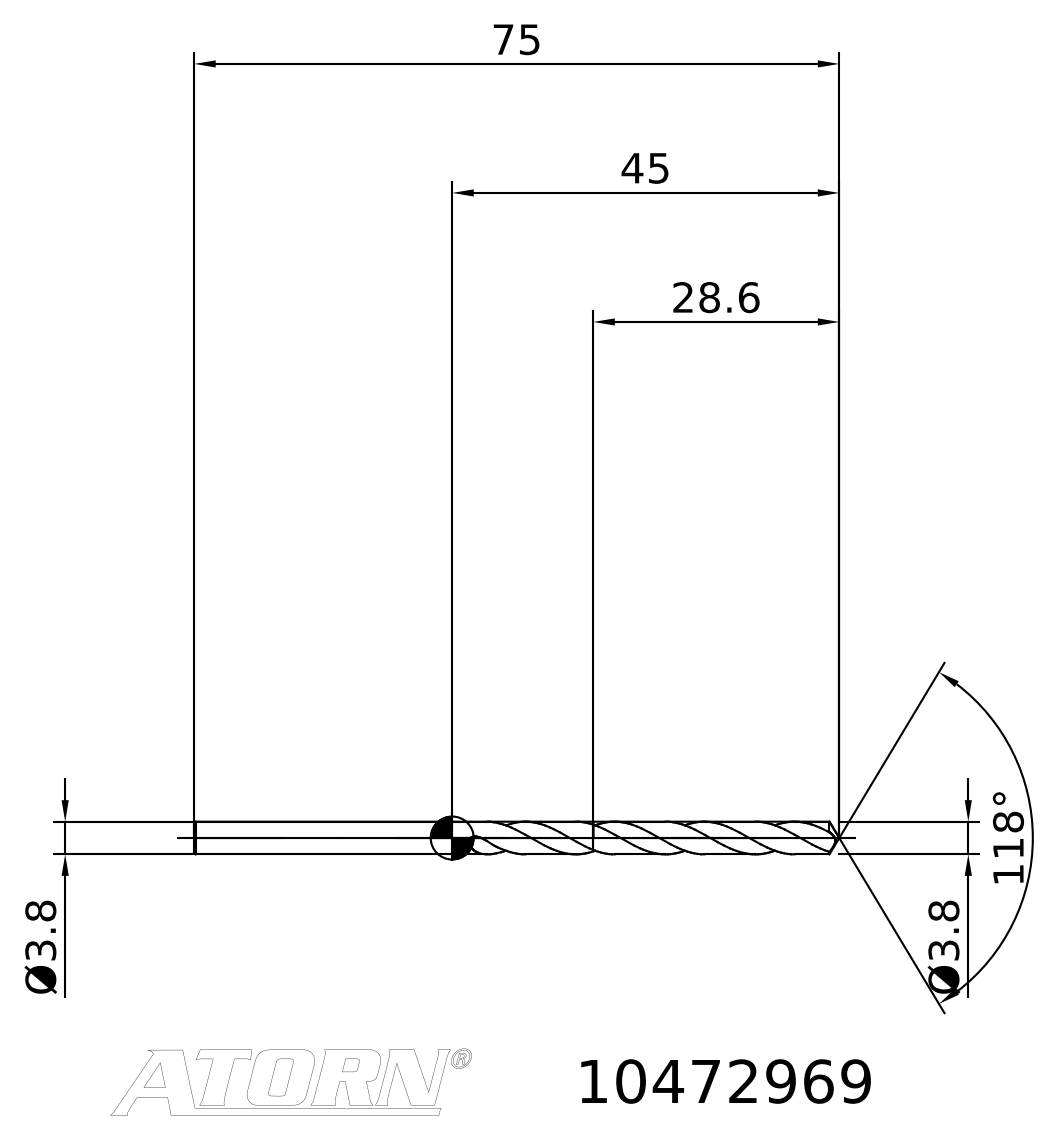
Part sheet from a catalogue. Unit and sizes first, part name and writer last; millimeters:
Units: millimetres
Overall size (bounding box): 75 × 4.47 × 3.8
Main face-to-face distances: 46.4
Volume: 680 mm³ · Surface area: 966 mm²
Bodies: 2 solids, 26 faces (3 planar, 0 cylindrical, 23 other)
STEP written by: TDM (AUTOMOTIVE_DESIGN)
